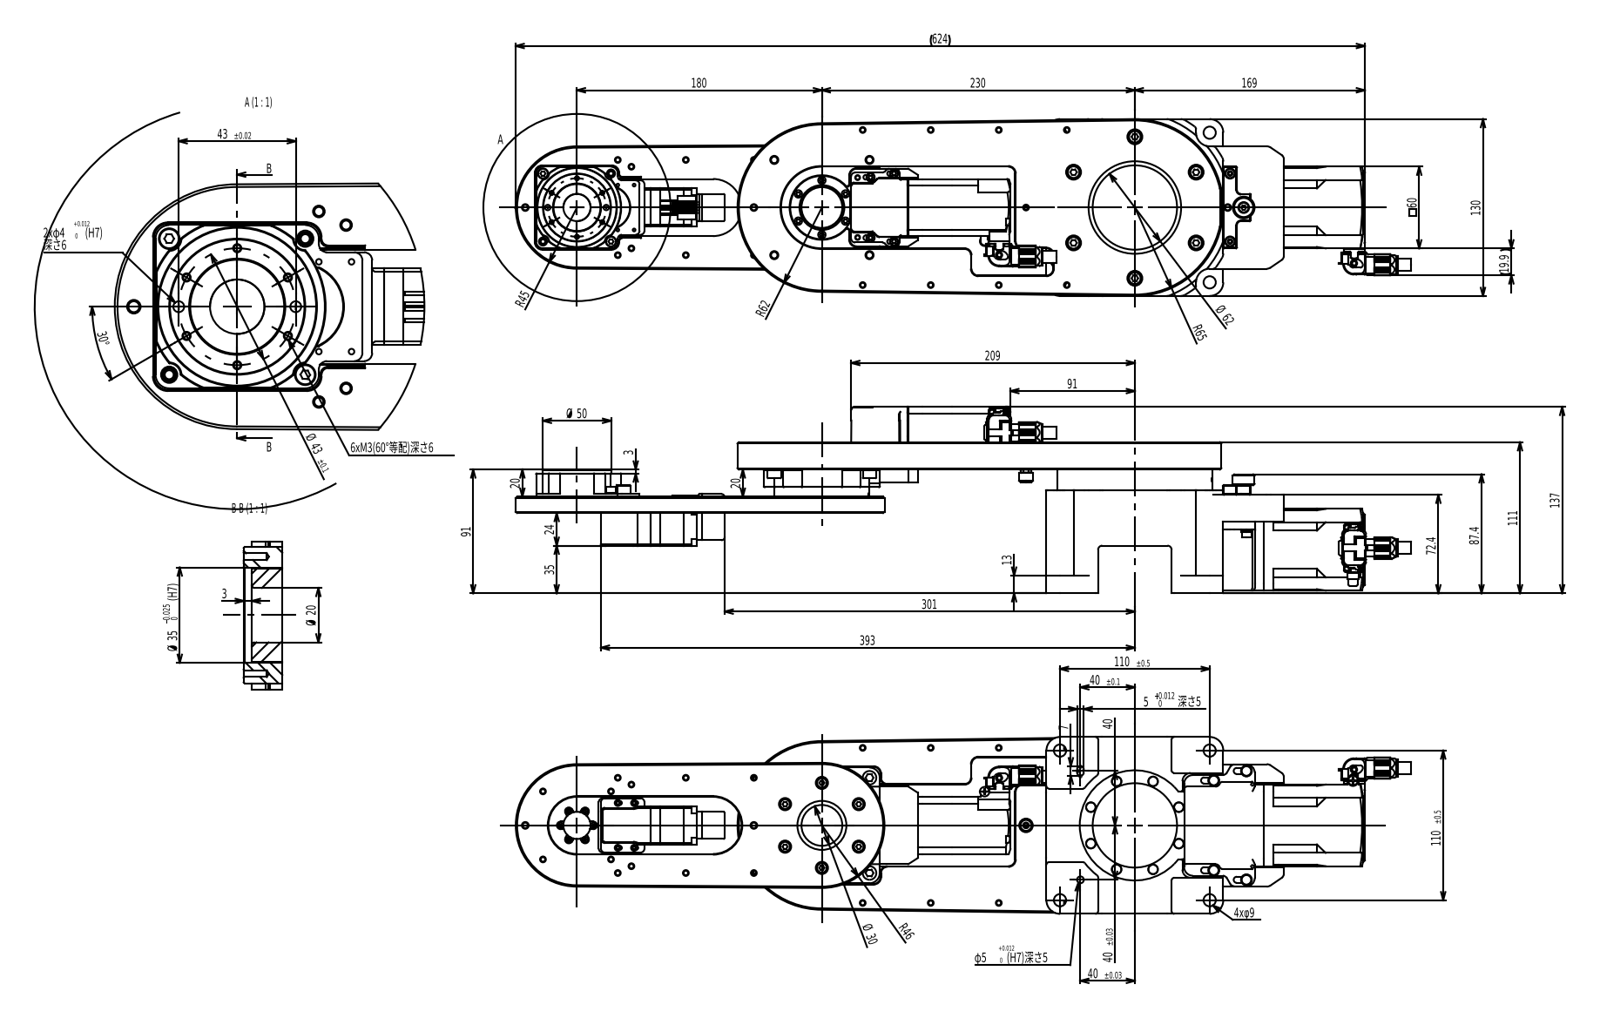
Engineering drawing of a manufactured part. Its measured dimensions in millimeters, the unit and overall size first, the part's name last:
Units: millimetres
Overall size (bounding box): 624 × 137 × 130
Round holes (diameter × count): ⌀3.3 ×20, ⌀2.5 ×16, ⌀4.5 ×14, ⌀5 ×13, ⌀2.05 ×10, ⌀3 ×8, ⌀4.2 ×7, ⌀8 ×7, ⌀3.4 ×6, ⌀5.5 ×6, ⌀10 ×6, ⌀4 ×5
Round bosses / shafts (diameter × count): ⌀7 ×24, ⌀4 ×13, ⌀4.3 ×8, ⌀3.5 ×8, ⌀8.5 ×6, ⌀7.6 ×6, ⌀3.98 ×6, ⌀3.3 ×6
Partial cylindrical surfaces — rounded edges, fillets, slot ends (radius × count): R2 ×51, R3 ×45, R2.5 ×35, R0.6 ×27, R1 ×27, R5 ×24, R6 ×22, R0.5 ×12
Main face-to-face distances: 20, 35, 17, 10, 3, 15, 13, 32, 36, 33
Hole centre spacings: 50, 52, 55.08, 120.31, 90.06, 124.48, 23, 26.92
Volume: 2 363 000 mm³ · Surface area: 437 012 mm²
Bodies: 58 solids, 2983 faces (1189 planar, 1077 cylindrical, 717 other)
Part name (STEP PRODUCT): OVR3041K3-H
STEP written by: SolidWorks 2020 (CONFIG_CONTROL_DESIGN)
